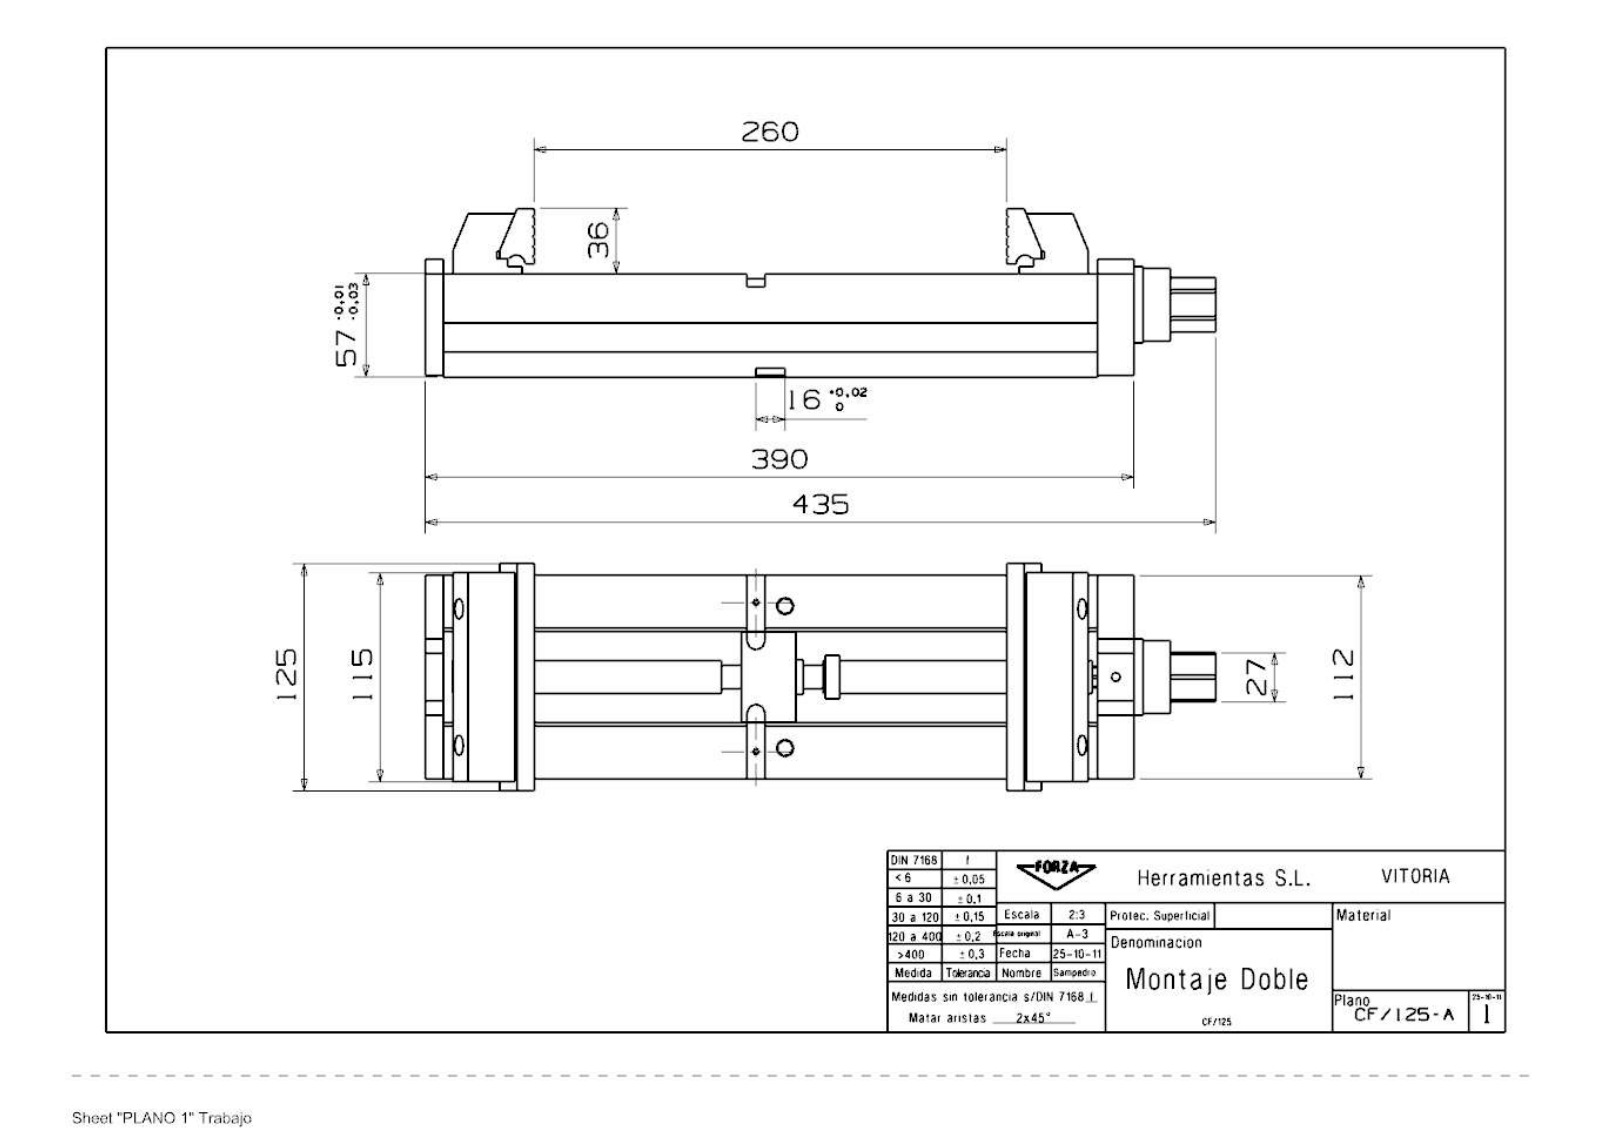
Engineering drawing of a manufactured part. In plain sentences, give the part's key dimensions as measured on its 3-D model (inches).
The part is named "30CF_125_Mordaza_Una". Its 3-D file was written by "SIEMENS PLM Software NX 7.5 (AUTOMOTIVE_DESIGN)". It is 17 solids with 666 faces: 409 planar, 205 cylindrical and 52 other. Overall it measures 17.126 by 4.921 by 3.659 inches. Its volume is 137.7 cubic inches and its surface area 622.3 square inches. Round holes: 11 of diameter 0.204, 4 of diameter 0.256, 4 of diameter 0.315, 3 of diameter 0.24, 3 of diameter 0.433, 2 of diameter 0.128, 2 of diameter 0.135, 2 of diameter 0.275, 2 of diameter 0.295, 2 of diameter 0.319, 2 of diameter 0.346, 2 of diameter 0.453. Round bosses or shafts: 3 of diameter 1.102, 1 of diameter 1.654, 1 of diameter 1.575, 1 of diameter 1.181, 1 of diameter 0.945, 1 of diameter 0.866, 1 of diameter 0.709, 1 of diameter 0.512. Partial cylindrical surfaces (rounded edges, fillets, slot ends): 20 of radius 0.012, 4 of radius 0.059, 4 of radius 0.197, 4 of radius 0.394, 2 of radius 0.315. The main face-to-face distances are 2.244, 0.774, 1.47, 3.504, 0.906, 1.969, 4.409, 1.22, 0.984, 0.728. The hole center spacings are 0.591, 2.362, 2.953, 0.028, 0.352, 0.362, 0.363, 0.394.
